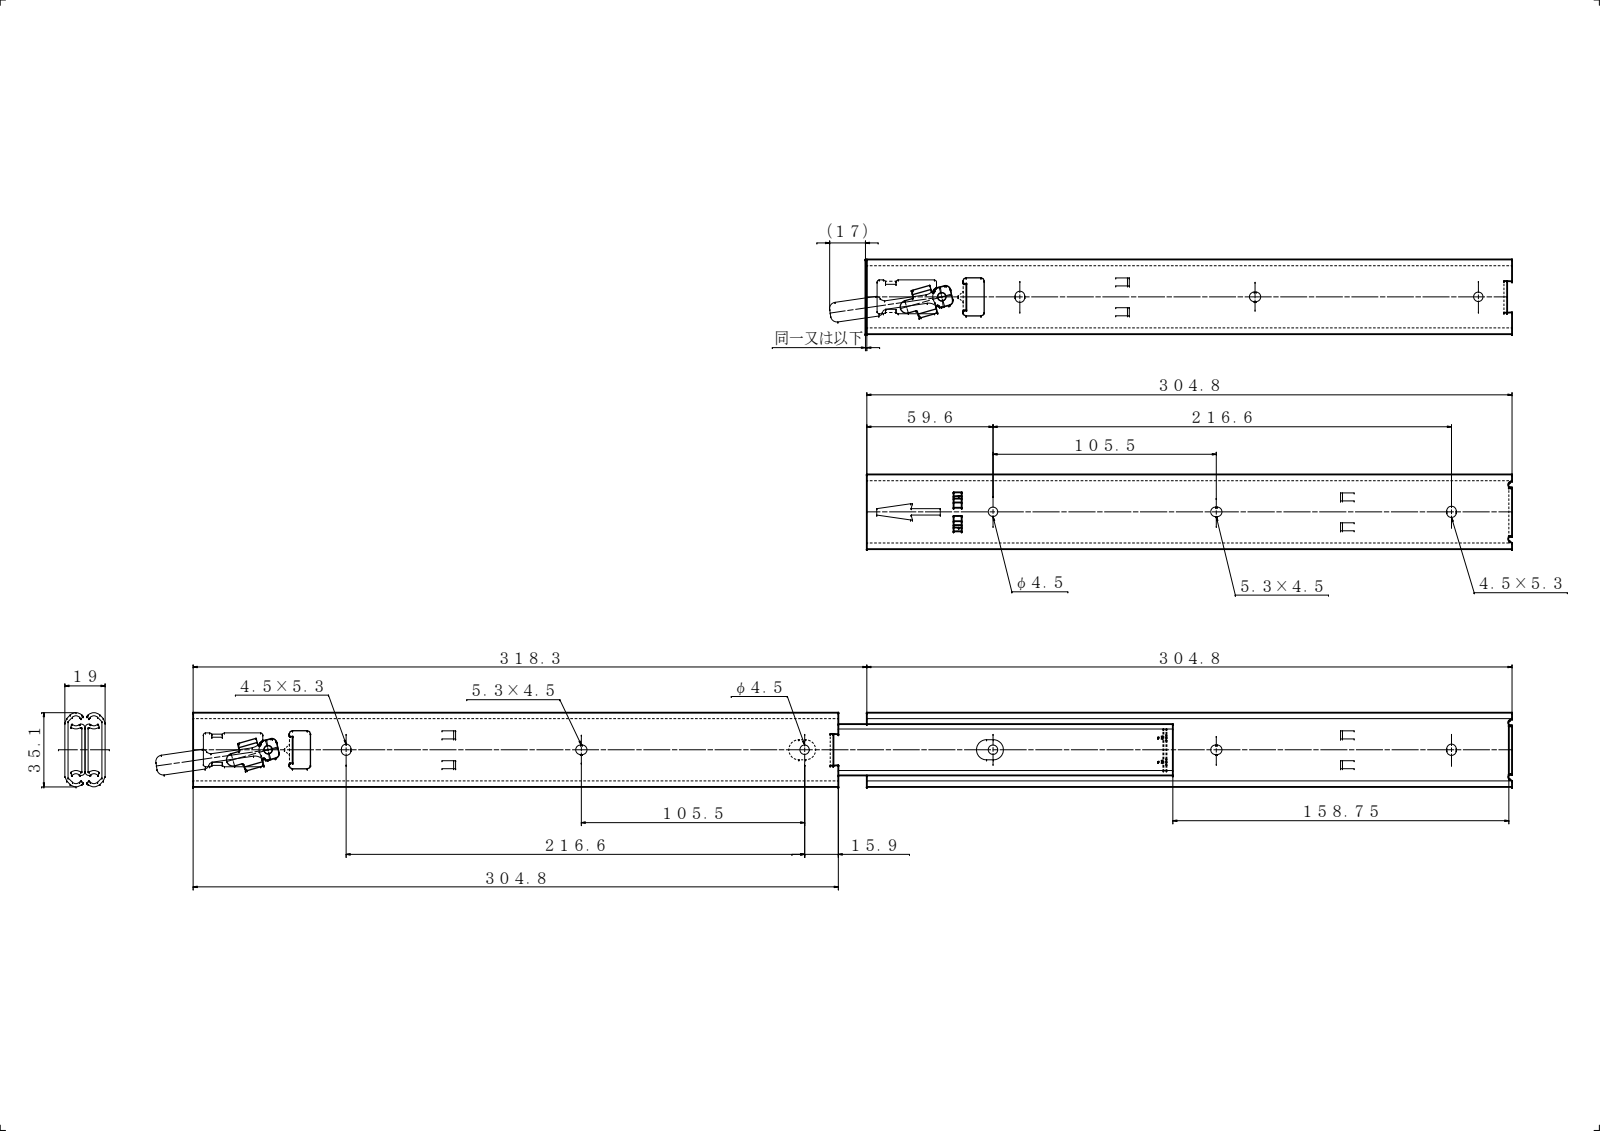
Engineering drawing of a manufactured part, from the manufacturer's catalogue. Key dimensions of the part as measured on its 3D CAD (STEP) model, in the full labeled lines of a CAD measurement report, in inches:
Part name (STEP PRODUCT): PN258 ロック; PN257 レバー; U31CL-12; OM-A U31CL-12 (+3 more)
STEP written by: SolidWorks 2019 (CONFIG_CONTROL_DESIGN)
Units: inches
Bodies: 7 solids, 417 faces (201 planar, 192 cylindrical, 24 other)
Overall size (bounding box): 25.236 × 1.382 × 0.748
Volume: 4.195 in³ · Surface area: 149.4 in²
Round holes (diameter × count): ⌀0.177 ×2, ⌀0.1 ×1, ⌀0.157 ×1
Round bosses / shafts (diameter × count): ⌀0.394 ×1, ⌀0.154 ×1
Partial cylindrical surfaces — rounded edges, fillets, slot ends (radius × count): R0.039 ×24, R0.079 ×20, R0.118 ×17, R0.02 ×13, R0.016 ×12, R0.089 ×8, R0.063 ×7, R0.059 ×5
Main face-to-face distances: 0.059, 0.315, 0.374, 0.689, 0.256, 0.433, 0.63, 0.748, 0.118, 1.185
Hole centre spacings: 3.504, 9.98, 13.484
